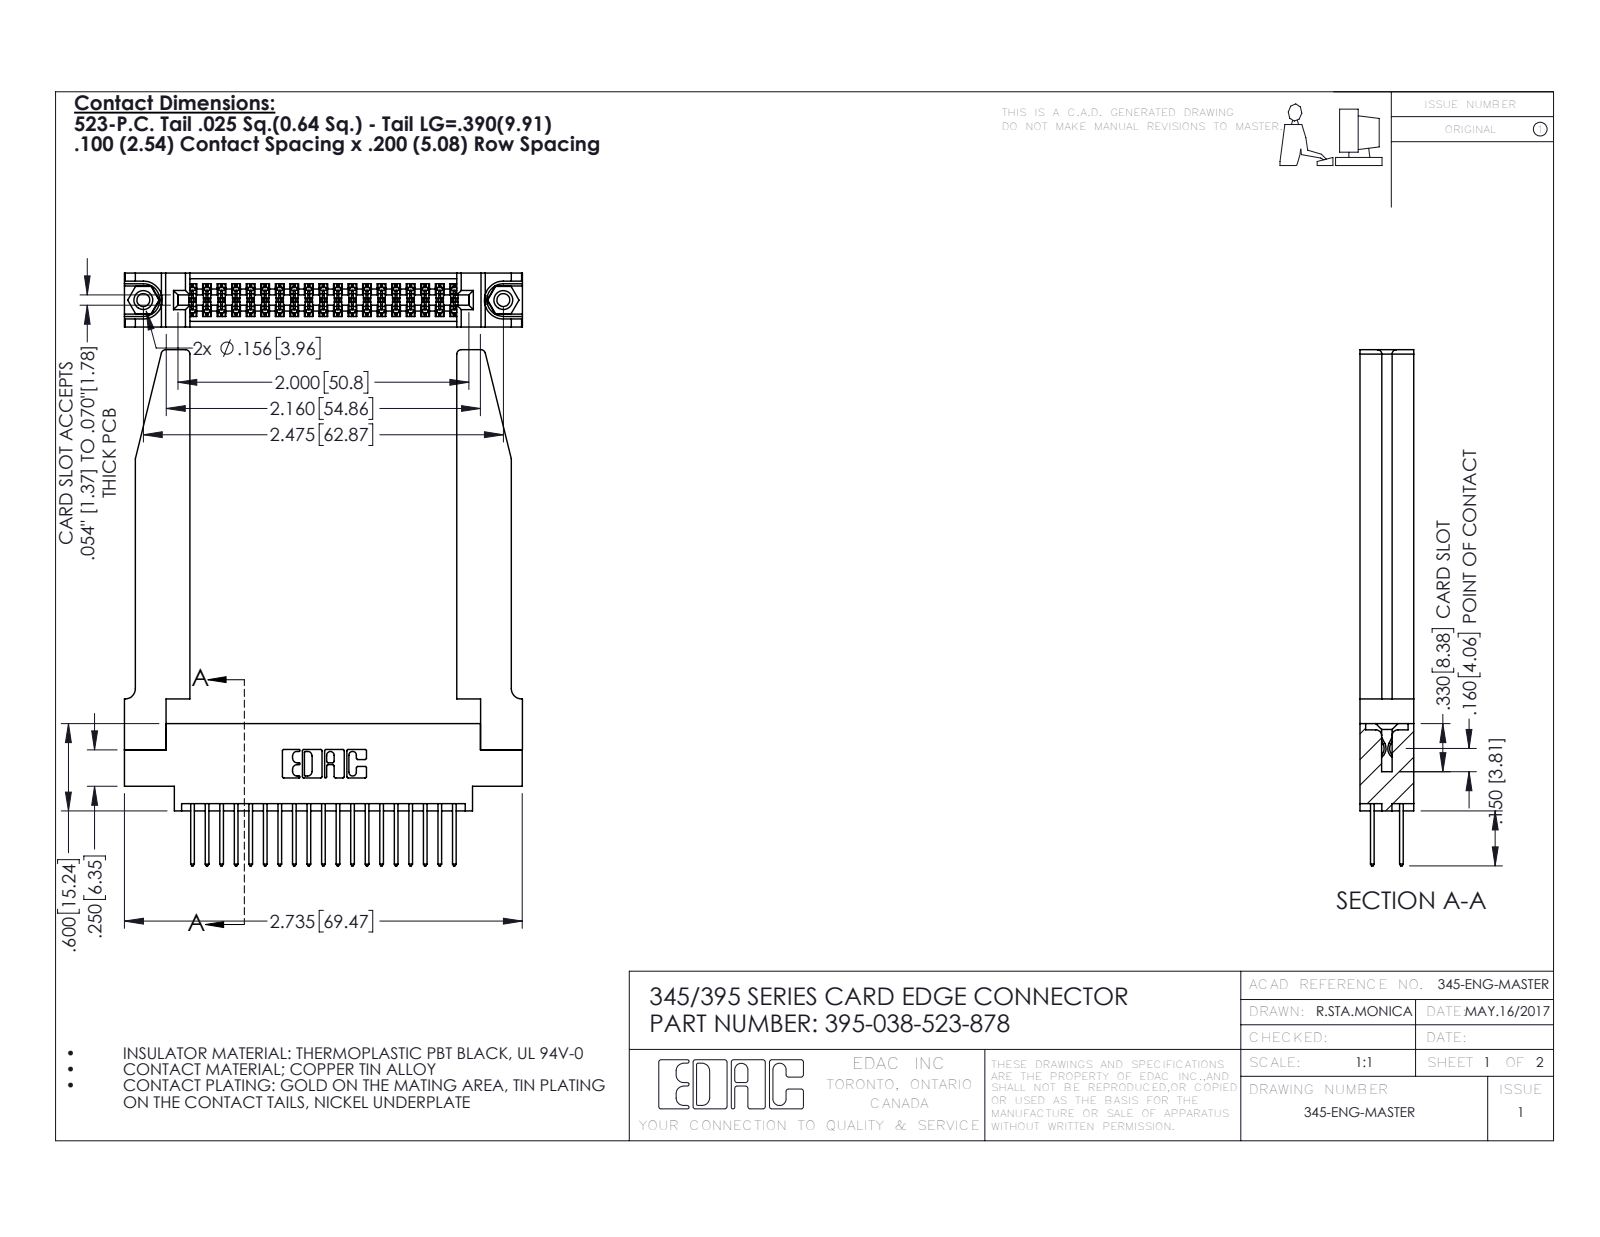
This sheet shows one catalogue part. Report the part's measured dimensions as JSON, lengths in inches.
{"part_name": "345-220-078_345-220-078; 345-250-001_345-250-001-102; 345-292-001_345-293-123; 345 Part_0.170 Offset - 0.156 Dia-TH (+1 more)", "step_written_by": "SolidWorks 2016 (CONFIG_CONTROL_DESIGN)", "units": "inches", "bodies": {"solids": 43, "faces": 2264, "planar": 1480, "cylindrical": 732, "other": 52}, "overall_size": [3.547, 2.736, 0.37], "volume_in3": 0.871, "surface_area_in2": 25.57, "round_holes": [[0.089, 2], [0.125, 2], [0.156, 2], [0.064, 1]], "round_bosses_or_shafts": [[0.155, 2]], "partial_cylinders_radius": [[0.006, 57], [0.01, 38], [0.01, 22], [0.03, 8], [0.007, 6], [0.031, 6], [0.026, 3], [0.014, 2]], "face_to_face_distances": [0.37, 0.072, 0.298, 0.2, 0.098, 0.272, 0.025, 0.225, 0.148, 0.15], "hole_center_spacings": [0.27, 2.241, 2.475]}
